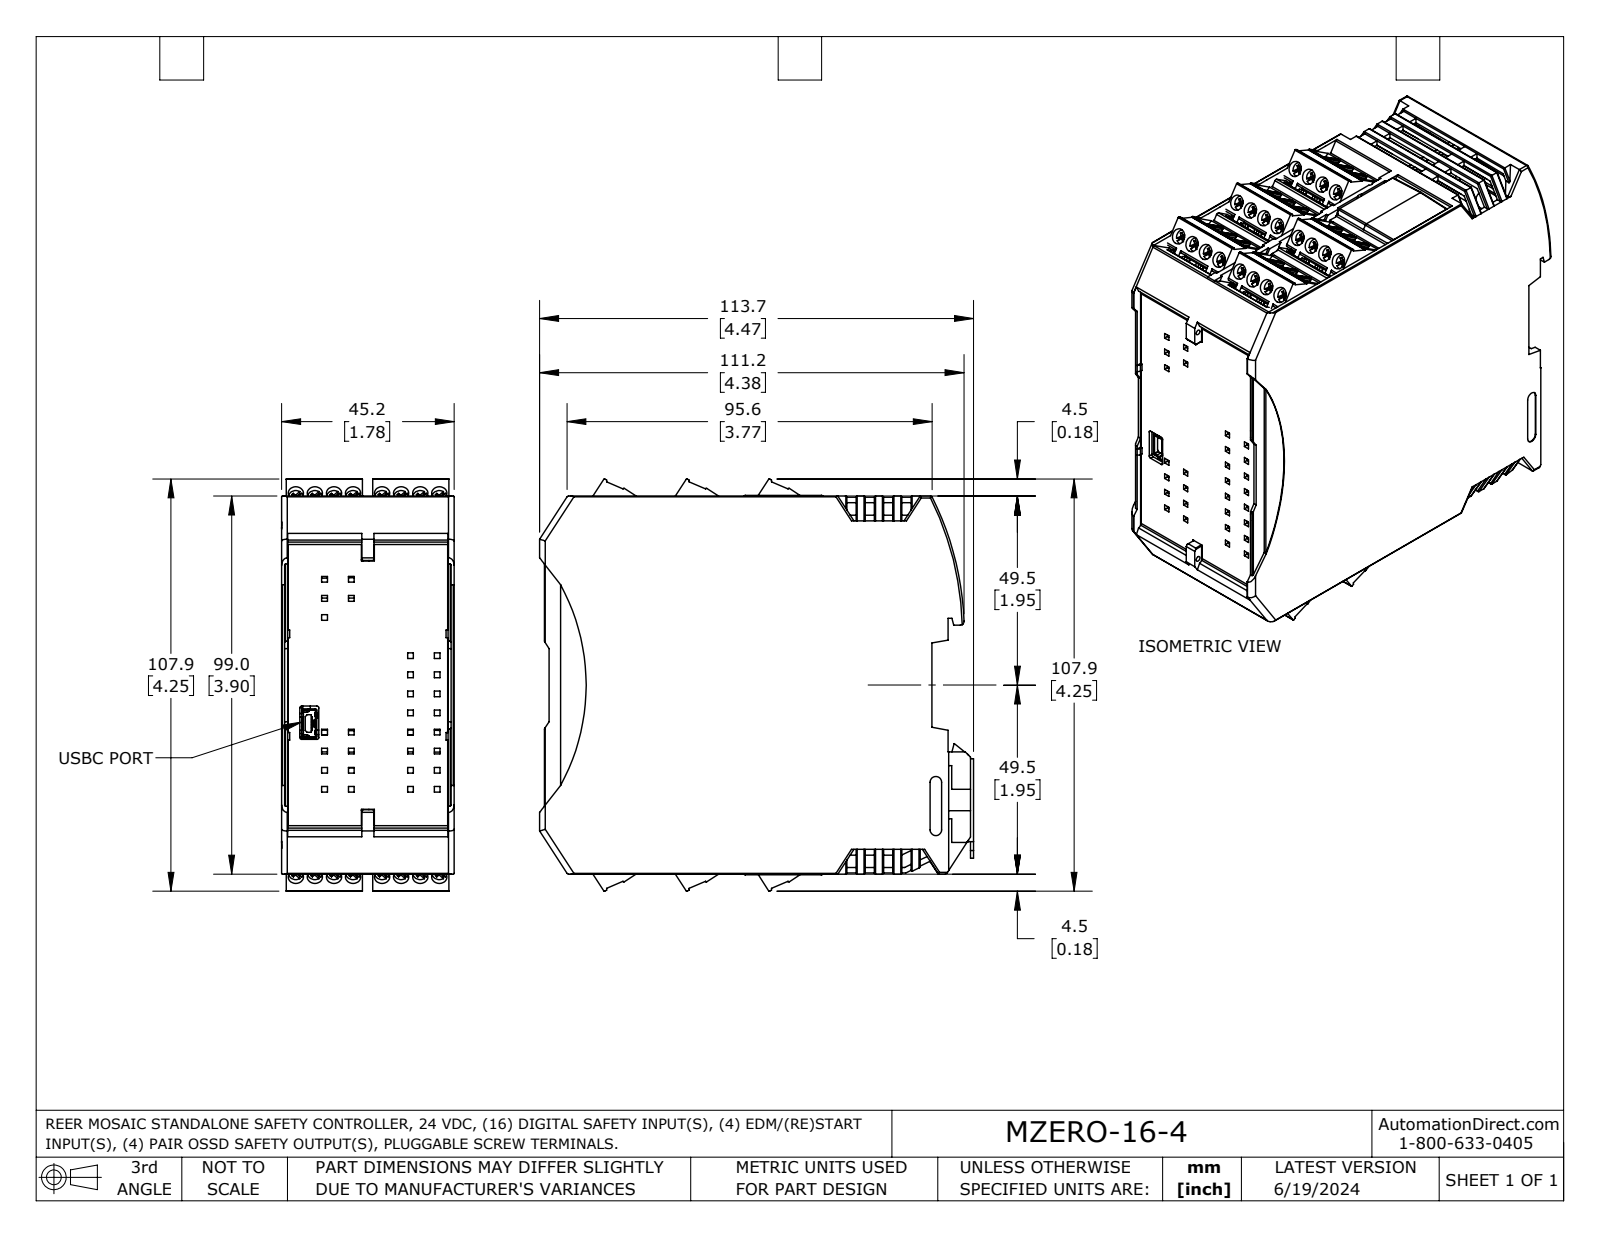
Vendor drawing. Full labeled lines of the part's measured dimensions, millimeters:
Part name (STEP PRODUCT): MZERO
STEP written by: SolidWorks 2023 (AUTOMOTIVE_DESIGN)
Units: millimetres
Bodies: 13 solids, 4573 faces (3691 planar, 847 cylindrical, 35 other)
Overall size (bounding box): 113.6 × 108 × 45.2
Volume: 92 230 mm³ · Surface area: 113 000 mm²
Round holes (diameter × count): ⌀1.4 ×41, ⌀2.8 ×40, ⌀4 ×40, ⌀3 ×8, ⌀1.3 ×1, ⌀3.2 ×1
Round bosses / shafts (diameter × count): ⌀3.8 ×40, ⌀0.8 ×2, ⌀6 ×1
Partial cylindrical surfaces — rounded edges, fillets, slot ends (radius × count): R0.3 ×132, R0.5 ×64, R2.9 ×40, R0.2 ×29, R0.8 ×21, R0.8 ×20, R1.5 ×20, R0.3 ×12
Main face-to-face distances: 1.2, 43.9, 45.2, 42.7, 1, 22.6, 18.1, 2, 21.4, 20.1
Hole centre spacings: 5, 10, 22.6, 12.8, 17.6, 18.8, 25.5, 27.6
